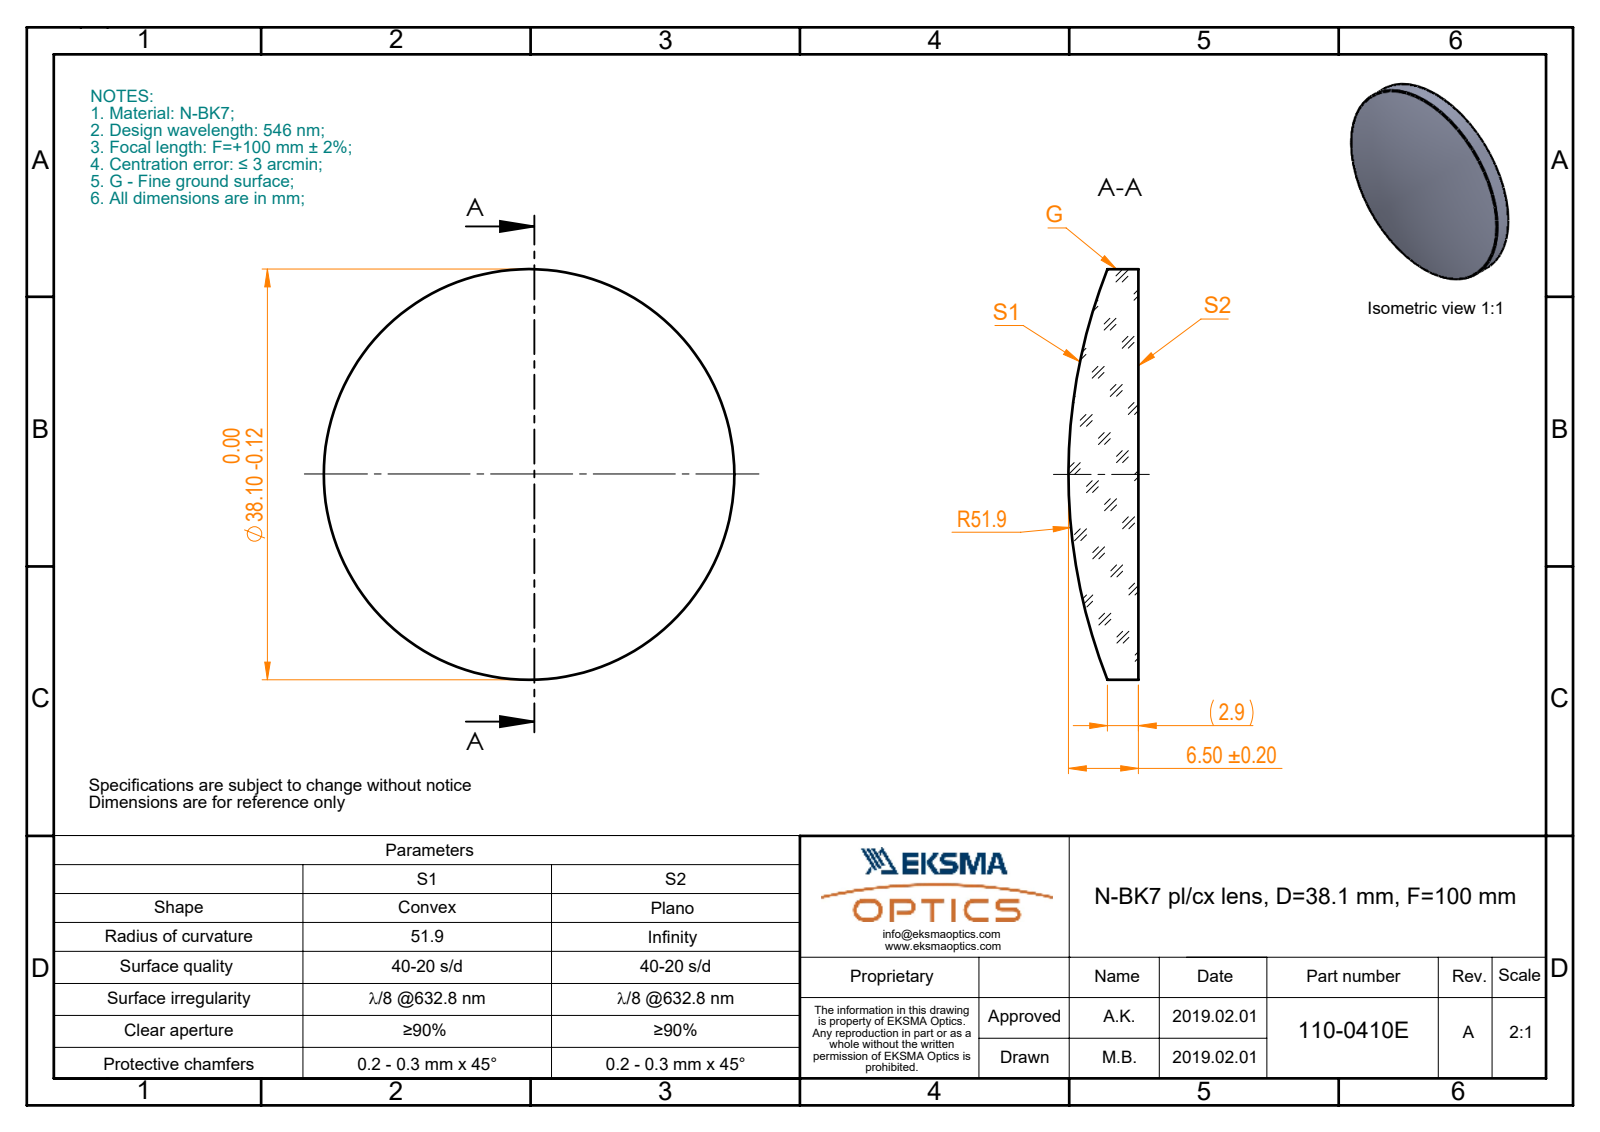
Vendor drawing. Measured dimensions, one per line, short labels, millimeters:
name: 110-0409E BK7 pl-cx 38.1 F100
written by: SolidWorks 2017 (CONFIG_CONTROL_DESIGN)
unit: mm
bodies: 1 solid, 5 faces (1 planar, 2 cylindrical, 2 other)
size: 38.1 × 38.1 × 6.5
volume: 5 369 mm³; area: 2 666 mm²
bosses: 1× ⌀38.1
